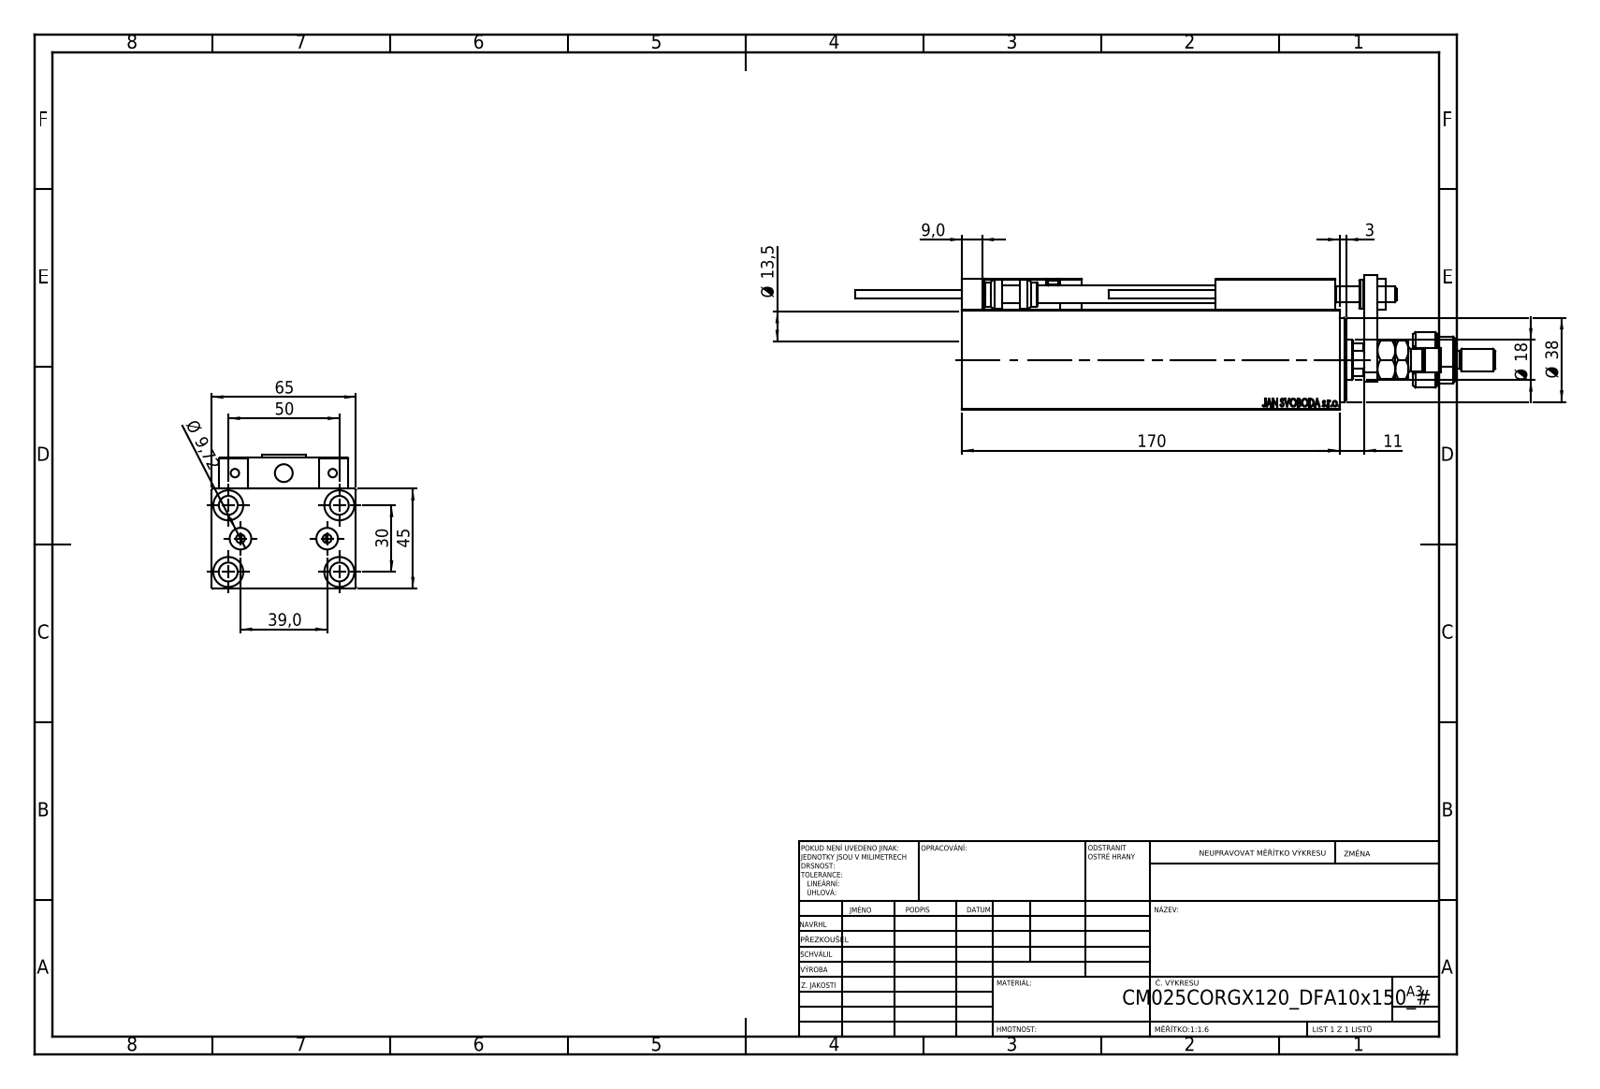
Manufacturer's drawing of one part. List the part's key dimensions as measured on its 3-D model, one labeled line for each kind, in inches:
Part name (STEP PRODUCT): SWITCH X; ALLEN BOLT D8; KONCOVKA; SWITCH_X_FRONT_BACK (+8 more)
STEP written by: SolidWorks 2019 (CONFIG_CONTROL_DESIGN)
Units: inches
Bodies: 25 solids, 1363 faces (588 planar, 197 cylindrical, 578 other)
Overall size (bounding box): 11.339 × 2.559 × 2.382
Volume: 29.56 in³ · Surface area: 196.1 in²
Round holes (diameter × count): ⌀0.157 ×6, ⌀0.315 ×5, ⌀0.335 ×5, ⌀0.126 ×4, ⌀0.531 ×4, ⌀0.197 ×2, ⌀0.383 ×2, ⌀0.276 ×1, ⌀0.571 ×1, ⌀0.709 ×1, ⌀0.846 ×1, ⌀1.063 ×1
Round bosses / shafts (diameter × count): ⌀0.197 ×2, ⌀0.15 ×2, ⌀0.984 ×1, ⌀0.827 ×1, ⌀0.63 ×1, ⌀0.512 ×1, ⌀0.433 ×1, ⌀0.394 ×1
Partial cylindrical surfaces — rounded edges, fillets, slot ends (radius × count): R0.012 ×30, R0.118 ×2, R0.217 ×1, R0.335 ×1, R0.344 ×1
Main face-to-face distances: 1.772, 2.559, 0.551, 0.236, 2.323, 0.118, 0.276, 7.126, 0.748, 0.512
Hole centre spacings: 0.629, 1.148, 1.849, 0.448, 0.768, 0.787, 1.138, 1.165
